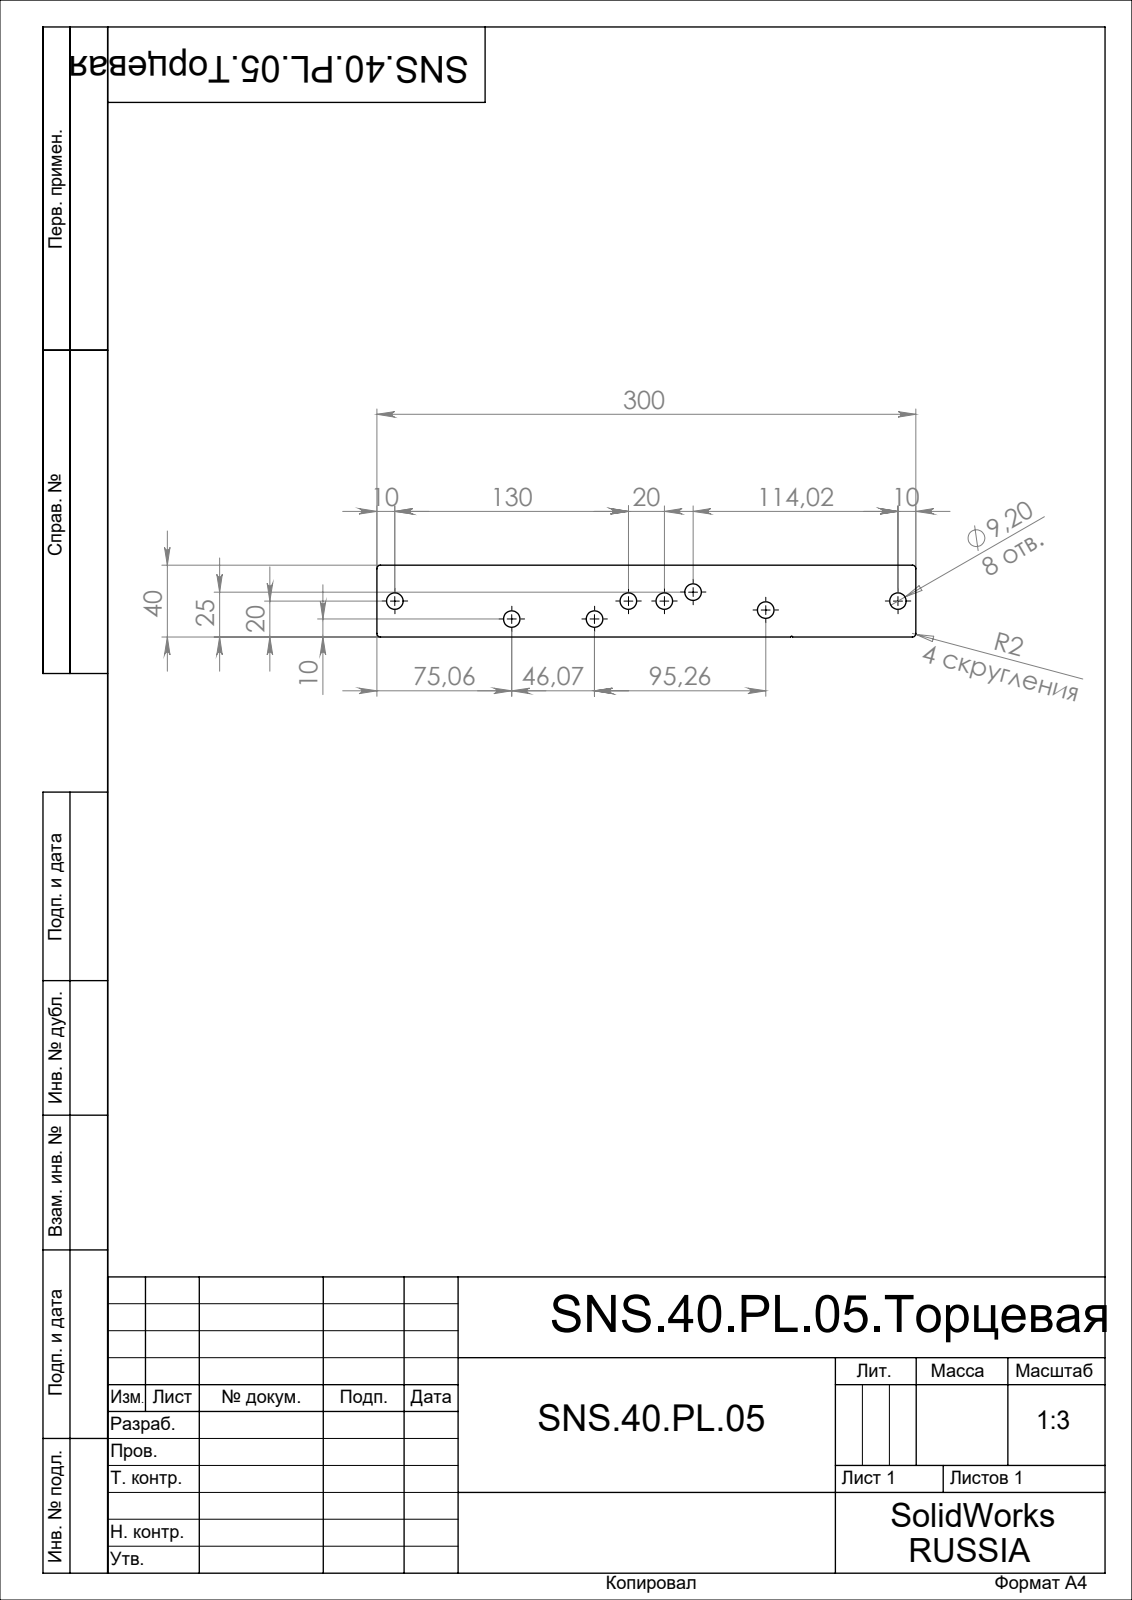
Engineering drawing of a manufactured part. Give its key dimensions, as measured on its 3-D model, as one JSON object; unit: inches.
{"step_written_by": "SolidWorks 2018 (AUTOMOTIVE_DESIGN)", "units": "inches", "bodies": {"solids": 1, "faces": 28, "planar": 7, "cylindrical": 21, "other": 0}, "overall_size": [11.811, 1.575, 0.197], "volume_in3": 3.498, "surface_area_in2": 42.58, "round_holes": [[0.362, 8]], "partial_cylinders_radius": [[0.079, 4], [0.02, 1]], "face_to_face_distances": [0.197, 1.575, 11.811], "hole_center_spacings": [5.118, 5.906, 0.659, 0.787, 0.841, 1.43, 1.58, 1.639]}
